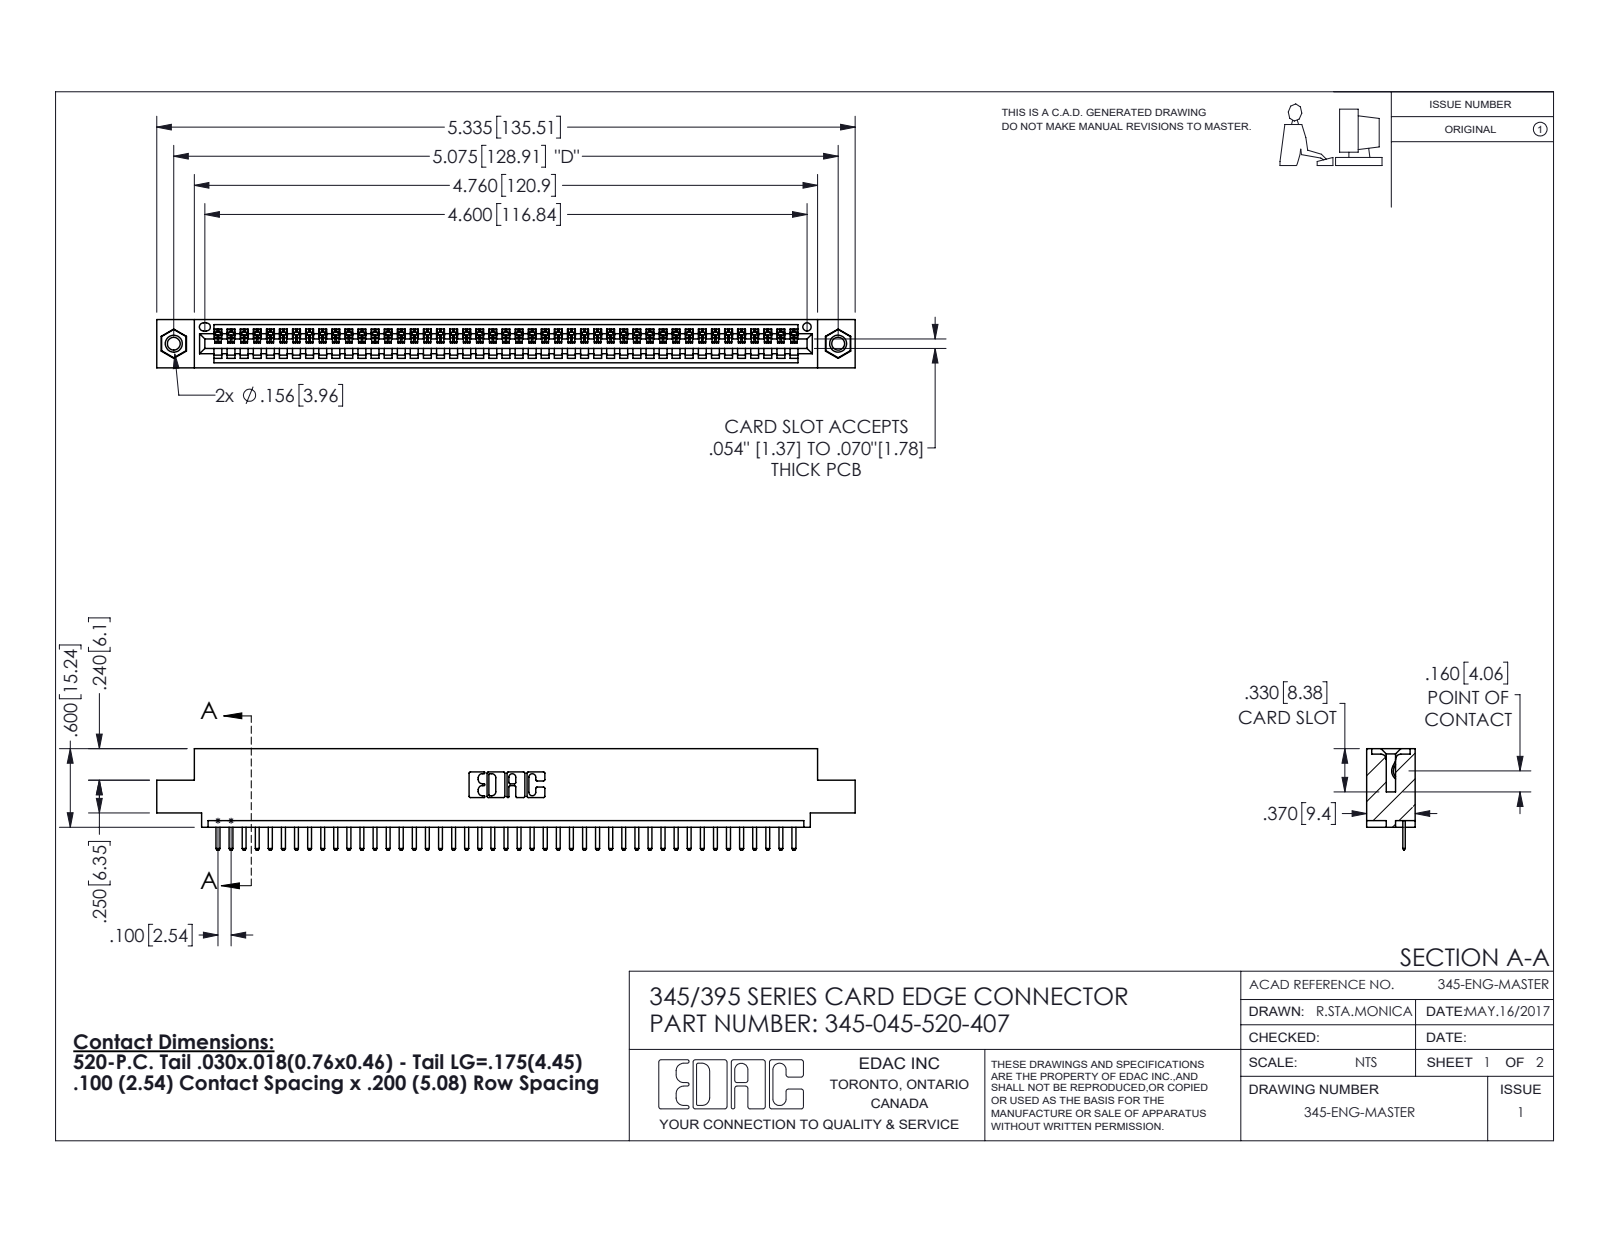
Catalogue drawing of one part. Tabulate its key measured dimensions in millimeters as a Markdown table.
| quantity | value |
| --- | --- |
| part name | 345-045-520-407; 345-250-001_345-250-005-103; 345-292-001_345-293-120; 345 Part_0.110 Offset - 0.156 Dia-TI |
| STEP written by | SolidWorks 2016 (CONFIG_CONTROL_DESIGN) |
| units | millimeters |
| bodies | 48 solids, 2980 faces (2006 planar, 958 cylindrical, 16 other) |
| overall size | 135.5 × 19.7 × 9.4 |
| volume | 12 700 mm³ |
| surface area | 16 580 mm² |
| round holes (diameter × count) | 2.5 × 2, 3.2 × 2, 4 × 2, 1.6 × 1 |
| round bosses / shafts (diameter × count) | 3.9 × 2 |
| partial cylindrical surfaces (radius × count) | 0.3 × 92, 0.2 × 90, 0.3 × 22, 0.2 × 6, 0.8 × 6, 0.7 × 3, 0.8 × 2, 1 × 2 |
| main face-to-face distances | 1.8, 7.6, 9.4, 5.1, 2.5, 6.9, 0.6, 5.7, 1.8, 3.8 |
| hole center spacings | 6.9, 122.9, 128.9 |
